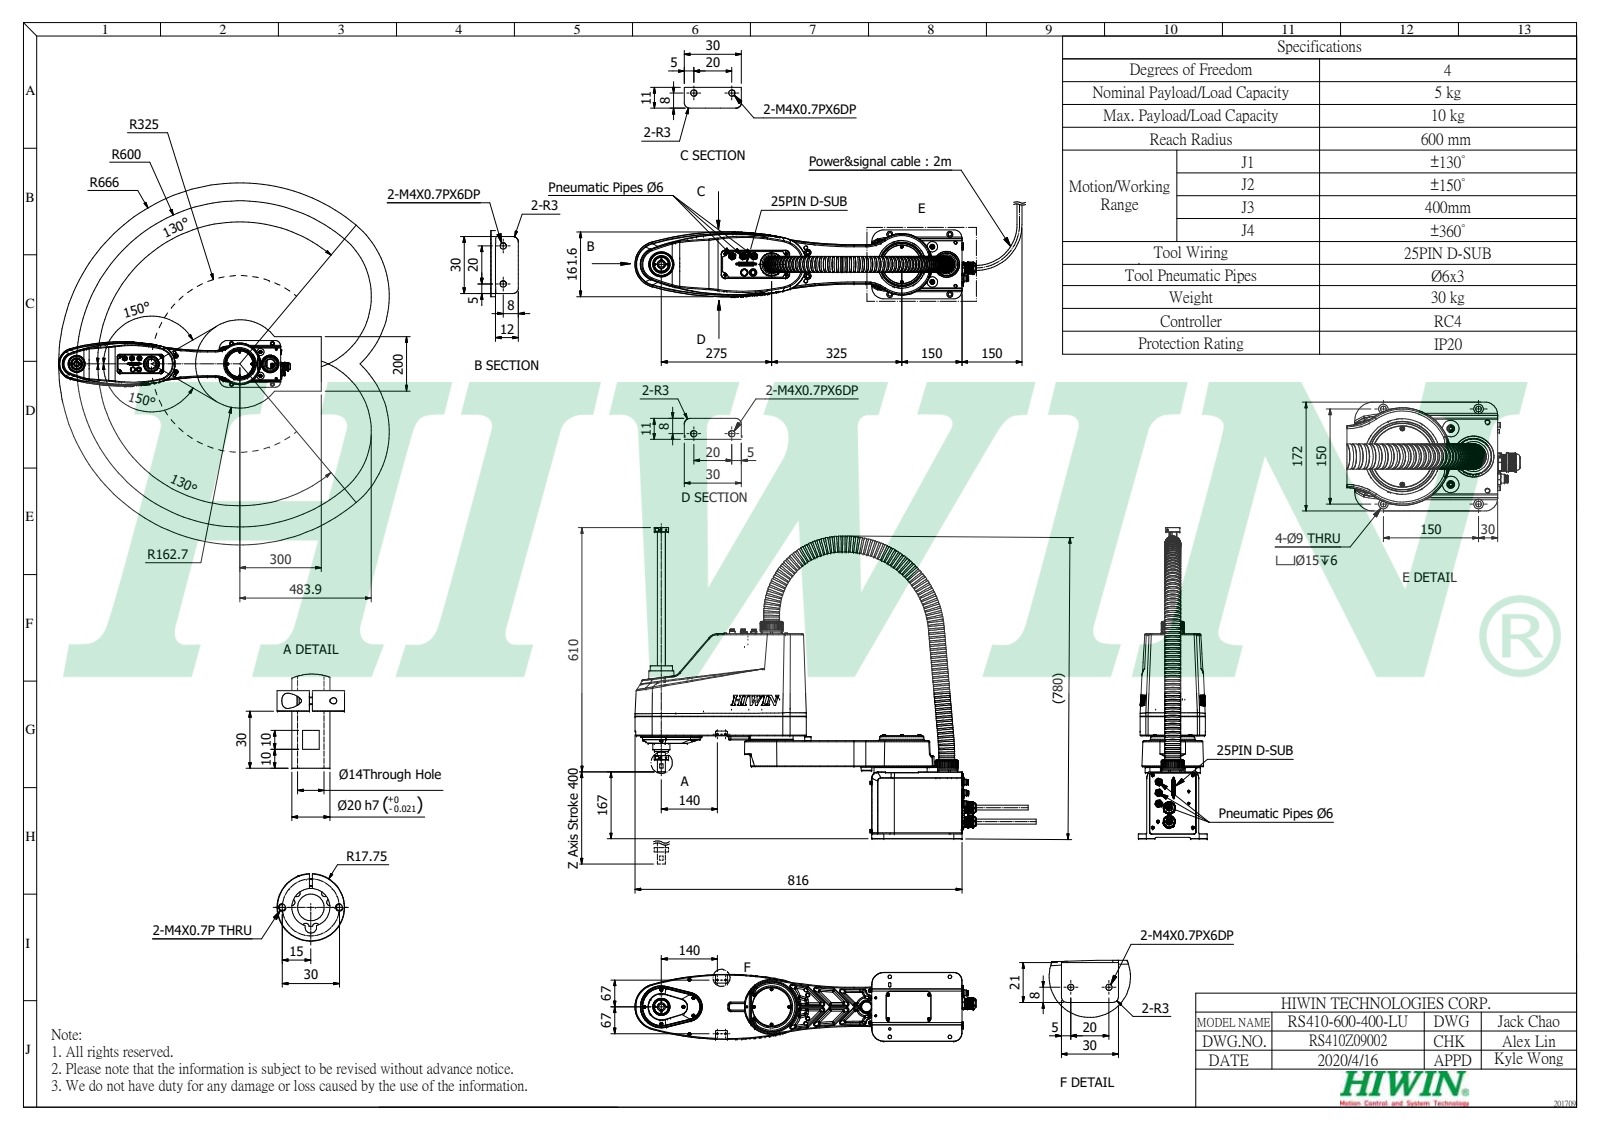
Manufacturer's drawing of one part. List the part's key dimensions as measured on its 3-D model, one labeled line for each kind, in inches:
Part name (STEP PRODUCT): RS410-600-400-LU; RS410-1; A1; B-600 (+1 more)
STEP written by: Autodesk Inventor 2020 (AUTOMOTIVE_DESIGN)
Units: inches
Bodies: 86 solids, 3304 faces (1583 planar, 825 cylindrical, 896 other)
Overall size (bounding box): 33.524 × 30.591 × 6.772
Volume: 1 353 in³ · Surface area: 2 336 in²
Round holes (diameter × count): ⌀0.128 ×8, ⌀0.13 ×8, ⌀0.177 ×8, ⌀0.354 ×8, ⌀0.433 ×8, ⌀0.33 ×6, ⌀0.157 ×2, ⌀3.197 ×2, ⌀0.591 ×1, ⌀0.677 ×1, ⌀0.787 ×1, ⌀2.362 ×1
Round bosses / shafts (diameter × count): ⌀1.575 ×84, ⌀1.496 ×84, ⌀0.276 ×55, ⌀0.157 ×31, ⌀0.217 ×20, ⌀0.472 ×8, ⌀0.394 ×8, ⌀0.551 ×6
Partial cylindrical surfaces — rounded edges, fillets, slot ends (radius × count): R0.079 ×43, R0.118 ×26, R0.008 ×24, R0.157 ×24, R0.197 ×21, R0.059 ×17, R0.031 ×11, R0.177 ×5
Main face-to-face distances: 0.079, 1.929, 2.008, 0.512, 5.118, 3.15, 0.472, 2.402, 5.551, 0.394
Hole centre spacings: 0.827, 1.019, 1.169, 1.609, 2.187, 2.516, 0.633, 0.633
